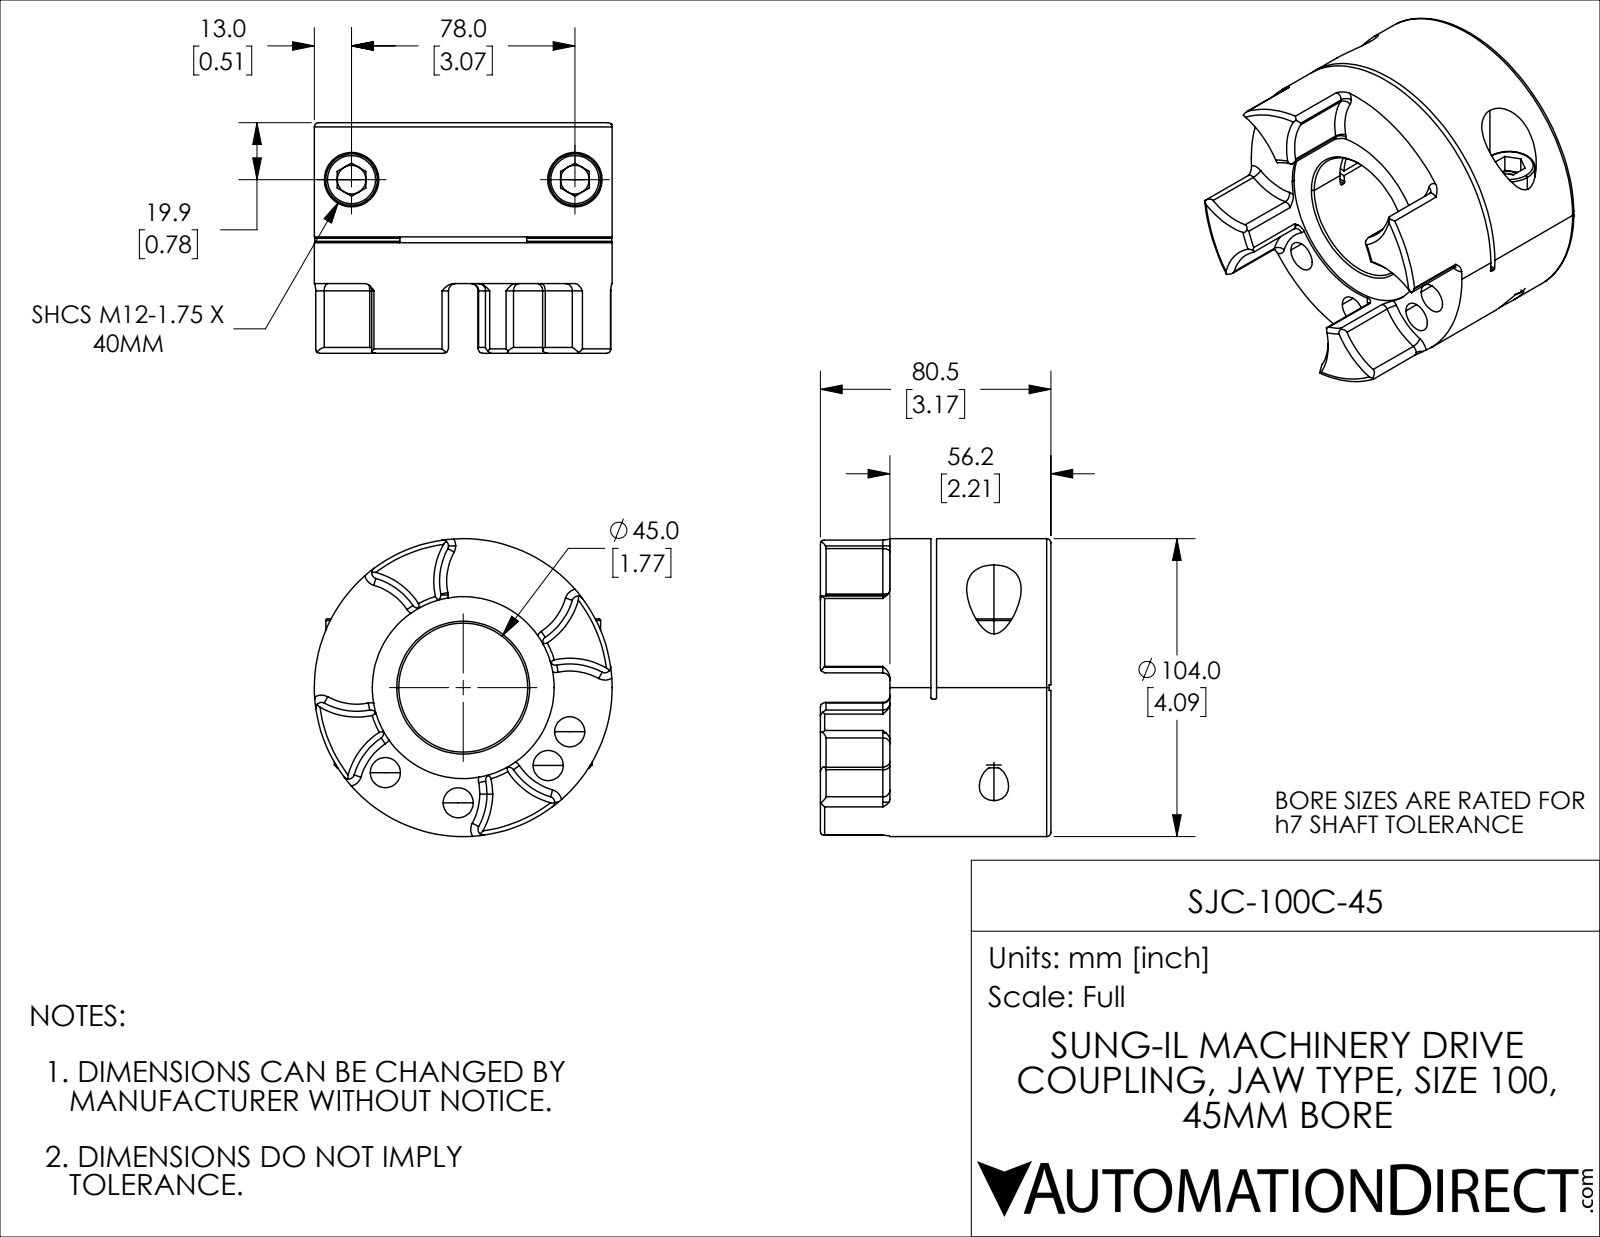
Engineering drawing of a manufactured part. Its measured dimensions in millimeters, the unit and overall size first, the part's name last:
Units: millimetres
Overall size (bounding box): 104 × 104 × 80.5
Round holes (diameter × count): ⌀10.5 ×4, ⌀10 ×2, ⌀10.2 ×2, ⌀12.5 ×2, ⌀19 ×2, ⌀45 ×1, ⌀63.5 ×1
Round bosses / shafts (diameter × count): ⌀18 ×2, ⌀12 ×2, ⌀104 ×1
Partial cylindrical surfaces — rounded edges, fillets, slot ends (radius × count): R2 ×16, R23.68 ×4, R0.5 ×2, R75 ×1
Main face-to-face distances: 2, 41.9, 39.9, 56.2, 16.3, 14.3, 55.3, 15.4, 13.4, 0.9
Hole centre spacings: 40.25, 13.98, 27.52, 34.03, 46.18, 56.92, 65.94, 78
Volume: 397 097 mm³ · Surface area: 70 241 mm²
Bodies: 3 solids, 215 faces (52 planar, 78 cylindrical, 85 other)
Part name (STEP PRODUCT): SJC-100C-45
STEP written by: SolidWorks 2021 (CONFIG_CONTROL_DESIGN)
